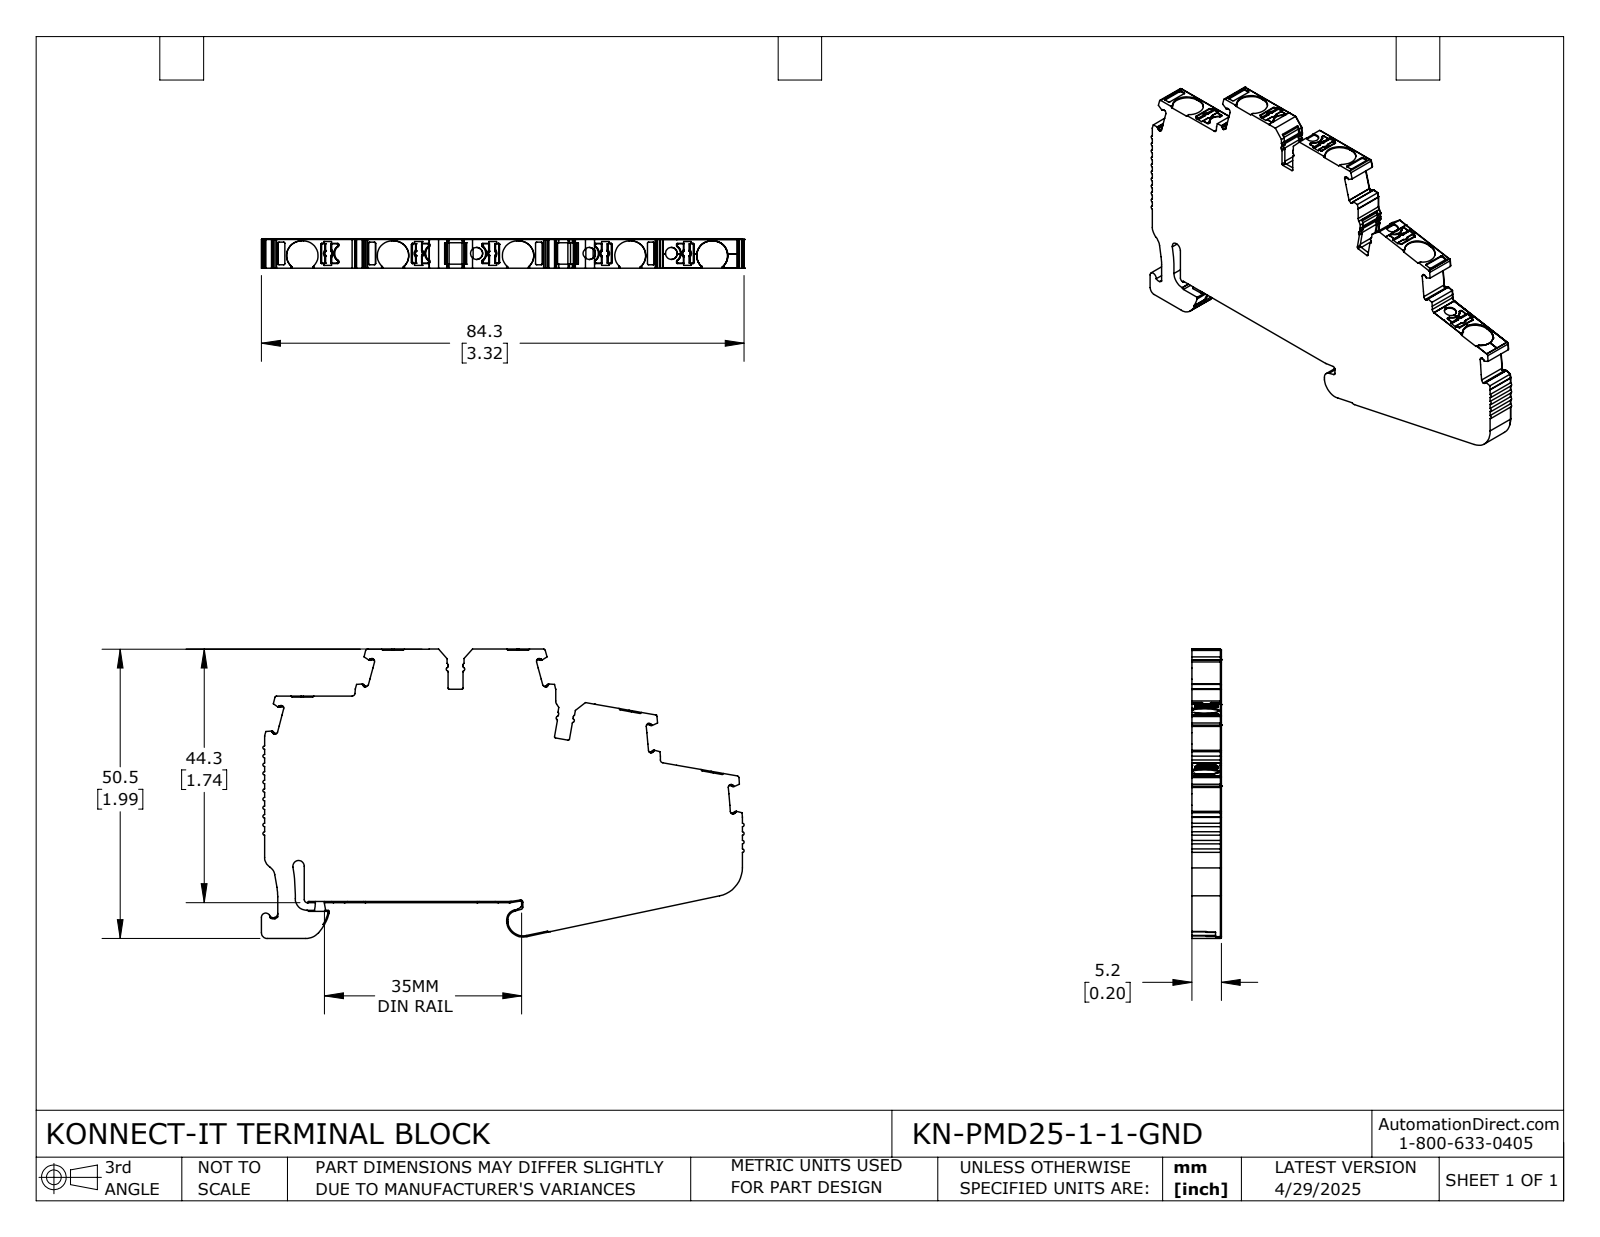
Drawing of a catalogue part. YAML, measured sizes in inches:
part_name: "KN-PMD25-1-1-GND"
step_written_by: "SolidWorks 2024 (CONFIG_CONTROL_DESIGN)"
units: inches
bodies: {solids: 1, faces: 1053, planar: 524, cylindrical: 444, other: 85}
overall_size: [3.318, 1.989, 0.203]
volume: 0.963
surface_area: 12.39
round_holes:
  - {diameter: 0.083, count: 3}
partial_cylinders:
  - {radius: 0.008, count: 92}
  - {radius: 0.012, count: 48}
  - {radius: 0.004, count: 33}
  - {radius: 0.006, count: 20}
  - {radius: 0.02, count: 19}
  - {radius: 0.016, count: 18}
  - {radius: 0.024, count: 12}
  - {radius: 0.006, count: 10}
face_to_face_distances: [0.203, 1.735, 1.412, 0.322, 1.734, 0.322, 0.079, 0.197, 0.246, 1.727]
hole_center_spacings: [0.628]
